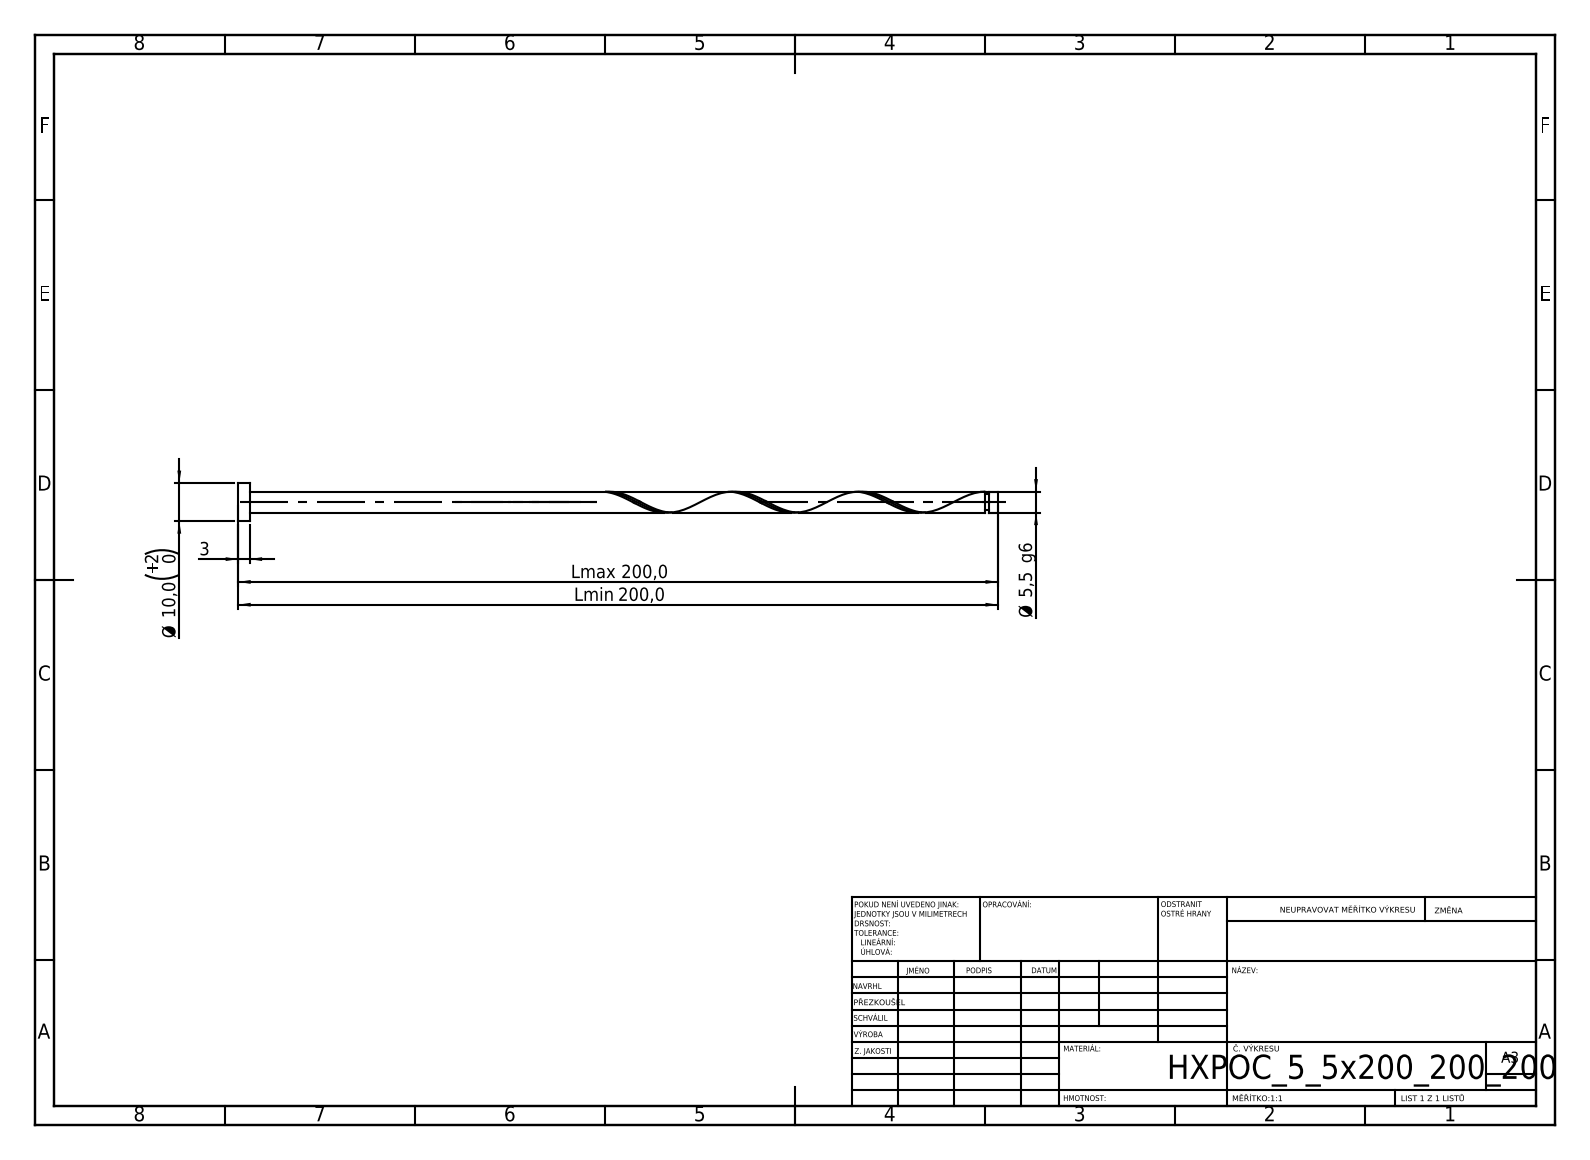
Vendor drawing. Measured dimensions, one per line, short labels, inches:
written by: SolidWorks 2019 (CONFIG_CONTROL_DESIGN)
unit: in
bodies: 1 solid, 21 faces (6 planar, 14 cylindrical, 1 other)
size: 7.874 × 0.394 × 0.394
volume: 0.297 in³; area: 5.782 in²
bosses: 1× ⌀0.394, 1× ⌀0.217, 1× ⌀0.173
face distances: 0.118, 7.874, 7.756, 7.783, 7.665, 0.091, 7.74, 7.622, 0.043, 0.134
